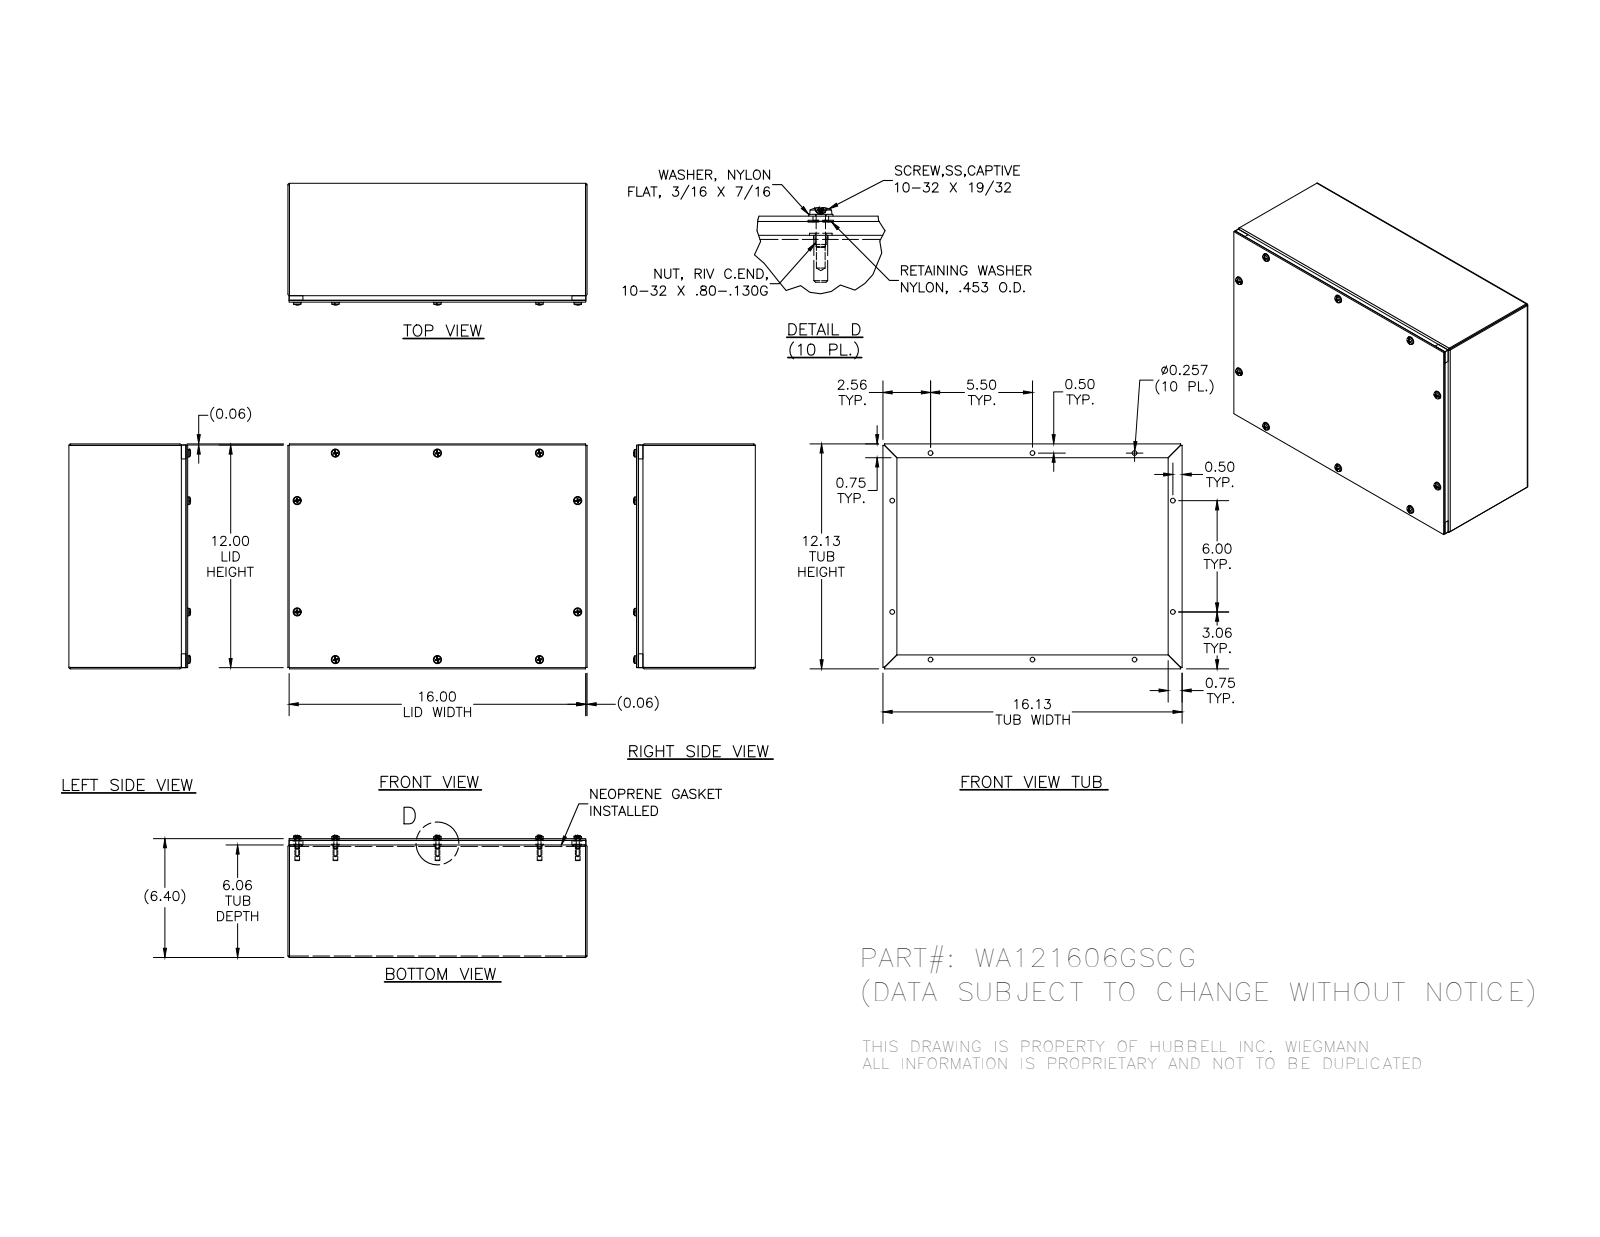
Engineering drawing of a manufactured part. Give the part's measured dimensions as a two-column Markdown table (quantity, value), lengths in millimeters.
| quantity | value |
| --- | --- |
| part name | WA121606GSCGBKP; 34984; WA121606GSCG; 37210 (+3 more) |
| STEP written by | SolidWorks 2014 (AUTOMOTIVE_DESIGN) |
| units | millimeters |
| bodies | 46 solids, 1070 faces (508 planar, 276 cylindrical, 286 other) |
| overall size | 409.6 × 308 × 166.6 |
| volume | 1 159 000 mm³ |
| surface area | 1 073 000 mm² |
| round holes (diameter × count) | 4 × 10, 4.8 × 10, 5 × 10, 6.5 × 10, 7.1 × 10, 7.1 × 10 |
| round bosses / shafts (diameter × count) | 11.5 × 10, 11.1 × 10, 10.3 × 10, 6.3 × 10, 4.2 × 10 |
| partial cylindrical surfaces (radius × count) | 2.3 × 10, 0.4 × 8, 2.3 × 8 |
| main face-to-face distances | 1.9, 2.4, 160.8, 158.4, 162.7, 160.3, 1.9, 152, 306.1, 308 |
| hole center spacings | 139.7, 279.4, 202.8, 223.7, 338.1, 338.1, 83.5, 83.5 |
